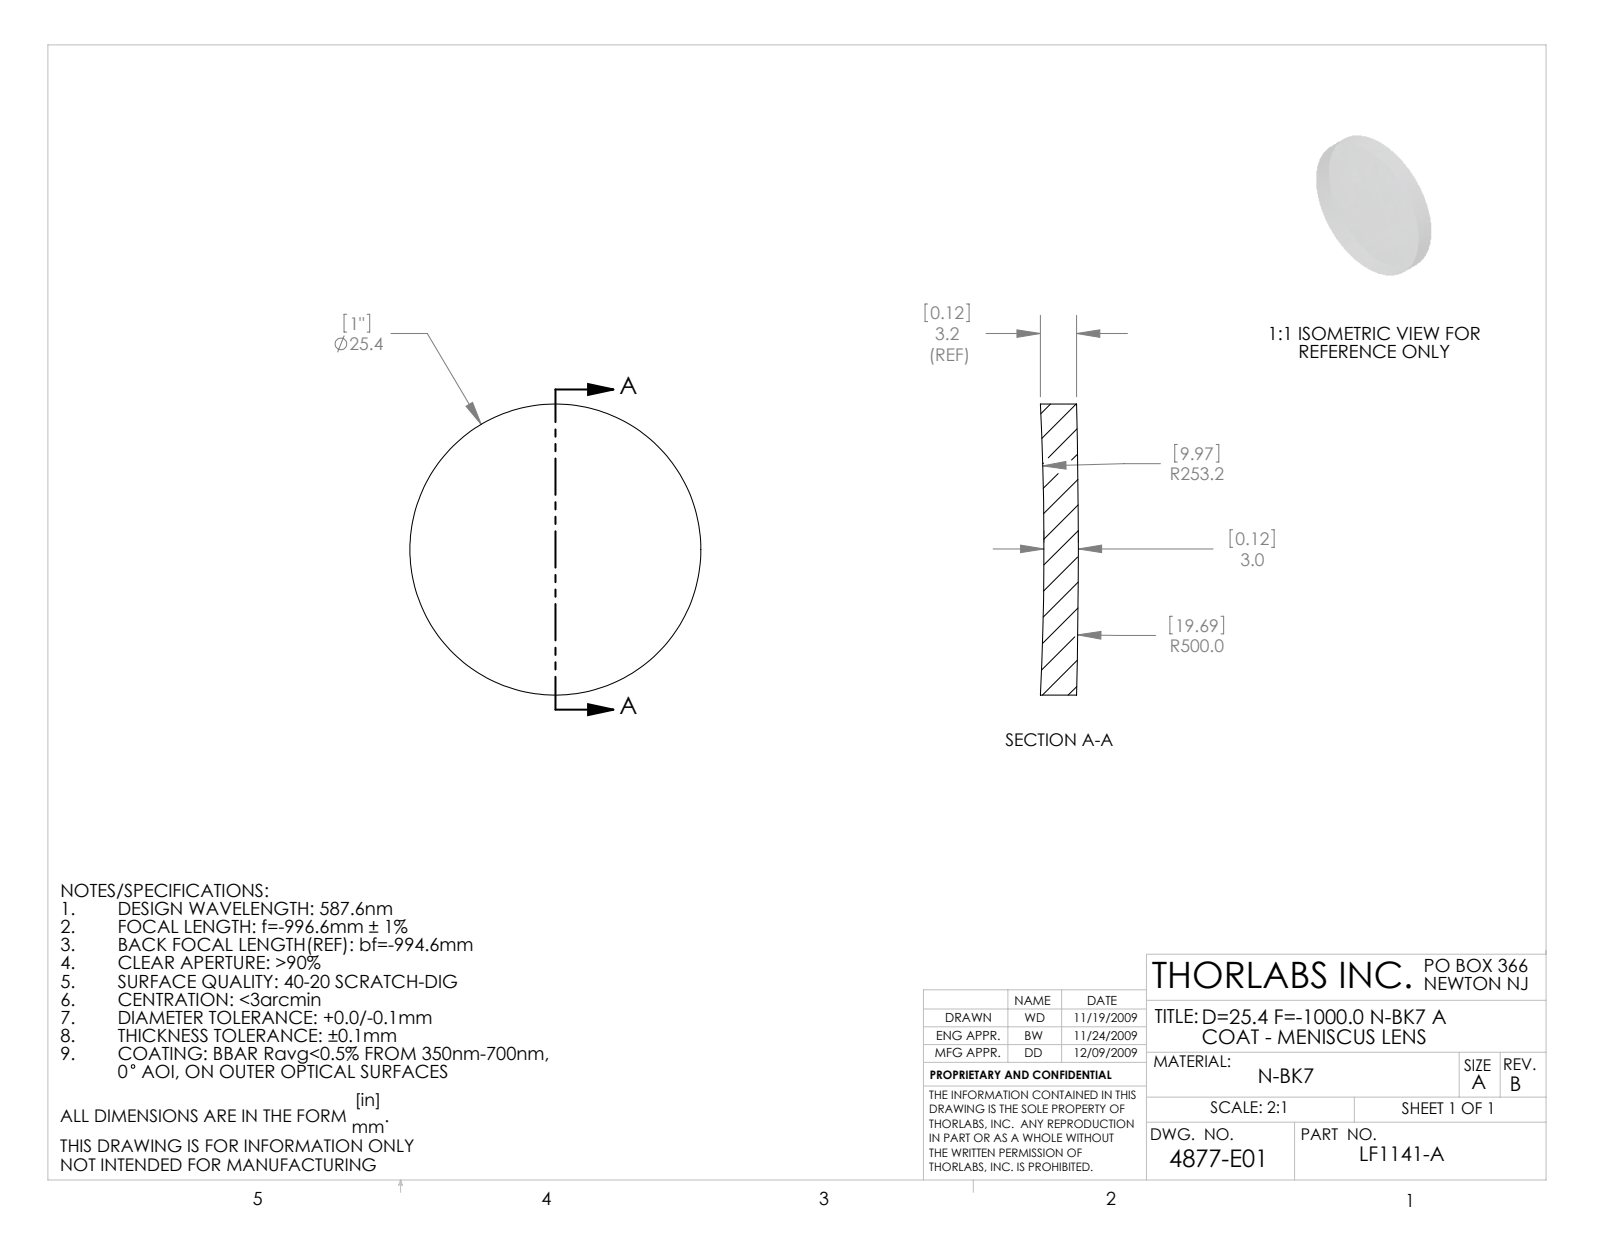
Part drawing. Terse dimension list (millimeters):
name: 4877-E0W
written by: SolidWorks 2009 (AUTOMOTIVE_DESIGN)
unit: mm
bodies: 1 solid, 6 faces (0 planar, 2 cylindrical, 4 other)
size: 25.4 × 25.4 × 3.32
volume: 1 560 mm³; area: 1 266 mm²
bosses: 1× ⌀25.4
